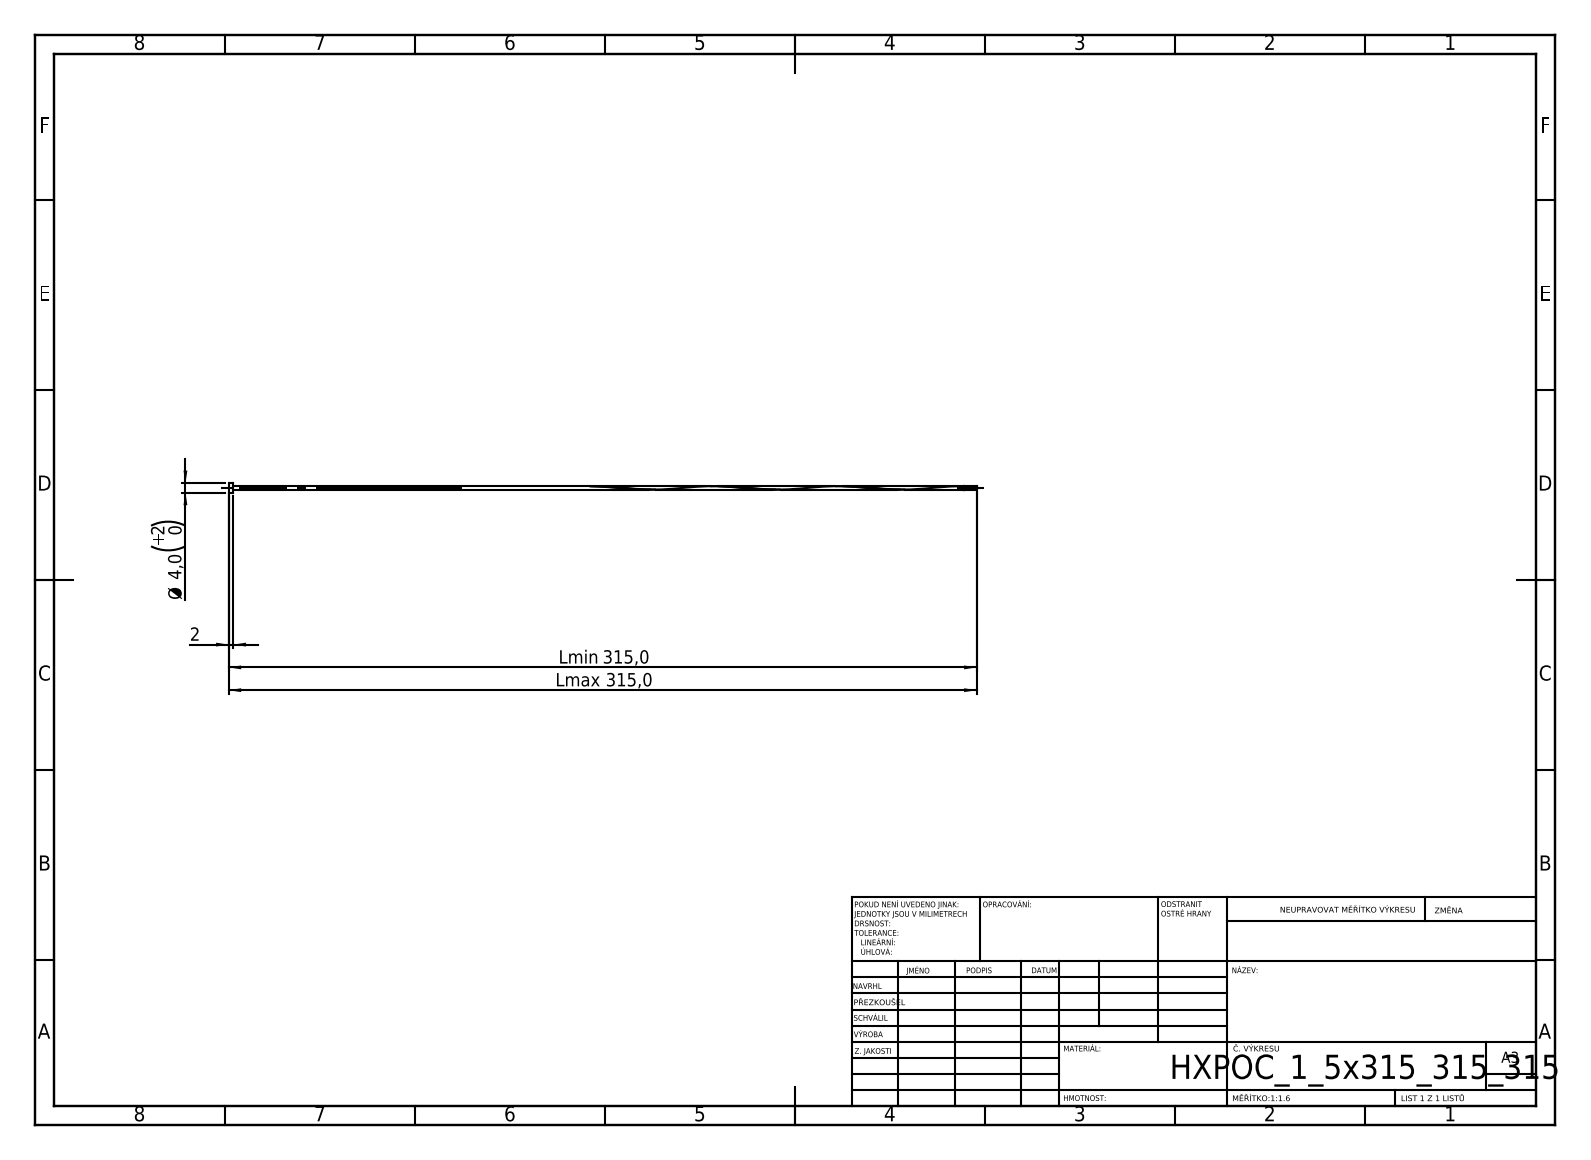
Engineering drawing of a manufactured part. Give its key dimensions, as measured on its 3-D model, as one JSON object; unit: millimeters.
{"step_written_by": "SolidWorks 2019 (CONFIG_CONTROL_DESIGN)", "units": "millimeters", "bodies": {"solids": 1, "faces": 16, "planar": 6, "cylindrical": 9, "other": 1}, "overall_size": [315, 4, 4], "volume_mm3": 696, "surface_area_mm2": 2043, "round_bosses_or_shafts": [[4, 1], [1.5, 1], [1.2, 1]], "face_to_face_distances": [2, 315, 313, 309.78, 307.78, 5.22, 309.48, 307.48, 5.52, 151.98]}
